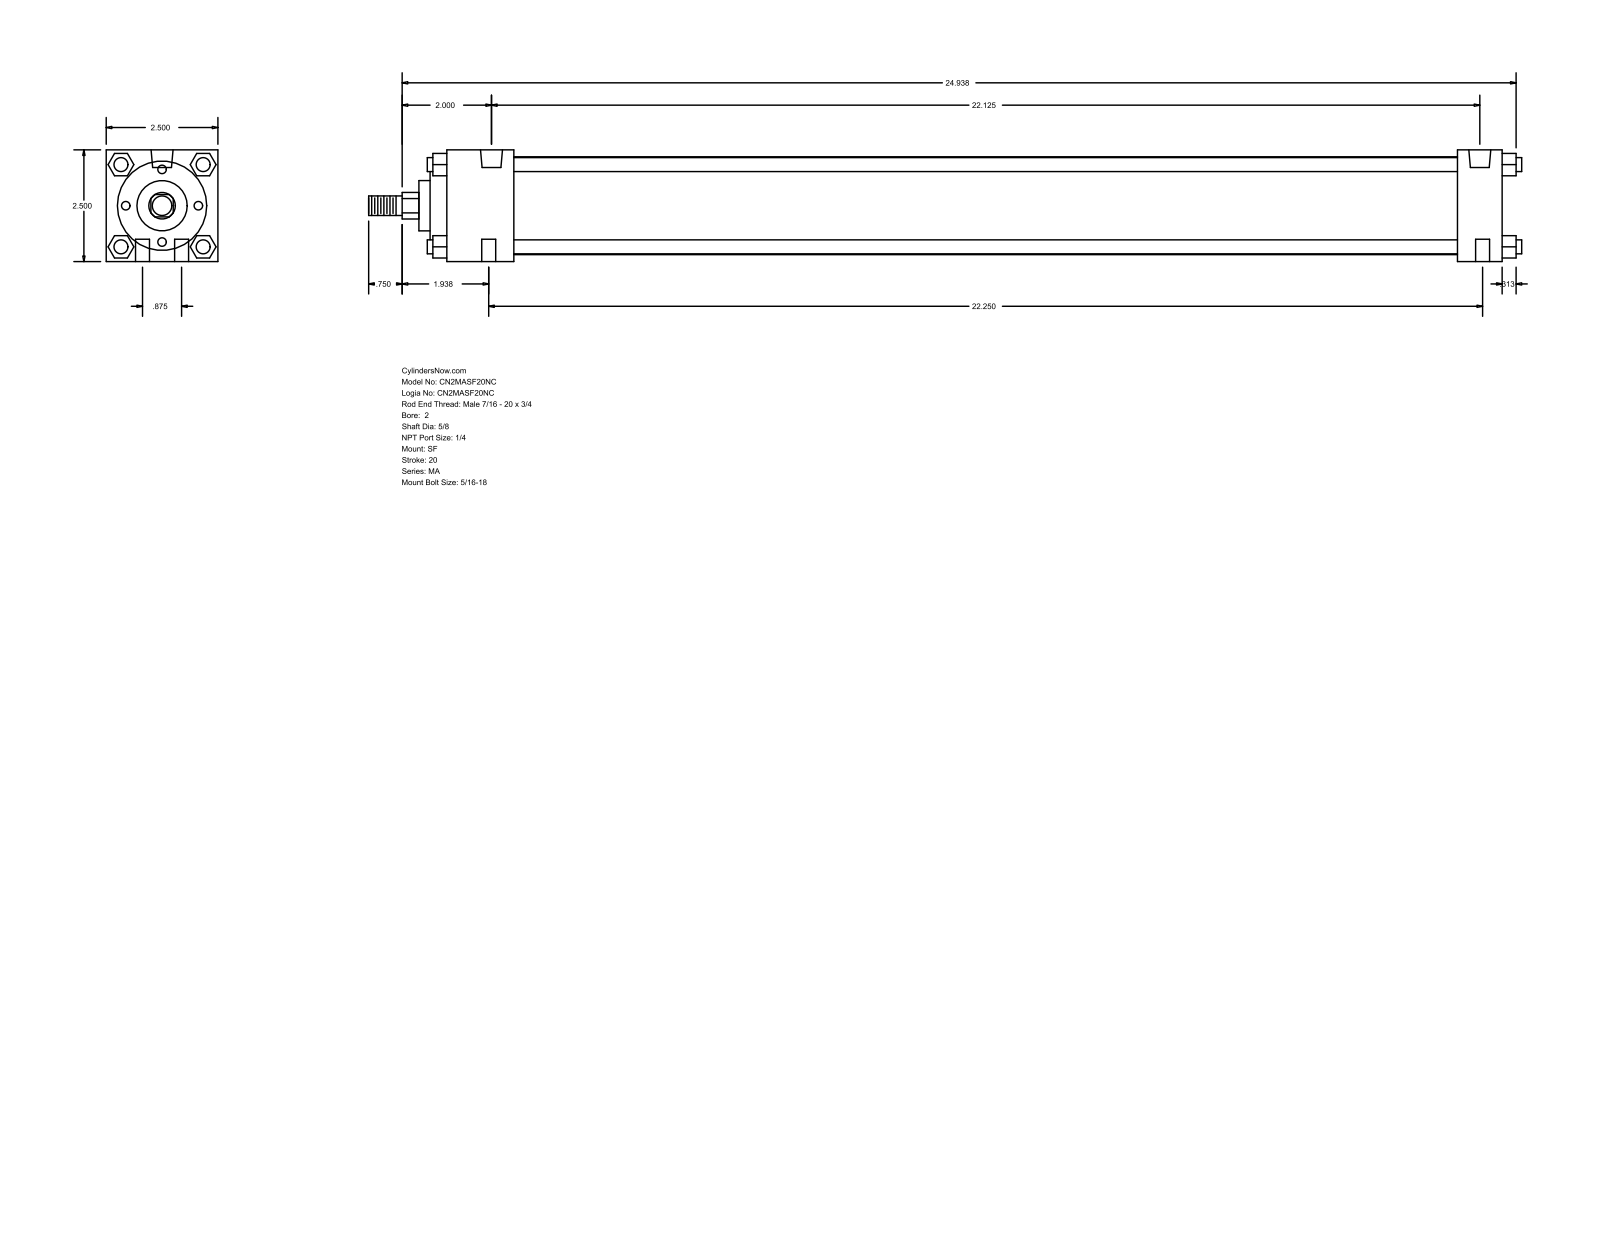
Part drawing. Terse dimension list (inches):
name: MA_SF__0200_0.625
written by: GSSL Pune (CONFIG_CONTROL_DESIGN)
unit: in
bodies: 0 solids, 126 faces (95 planar, 31 cylindrical, 0 other)
size: 25.813 × 2.5 × 2.5
holes: 6× ⌀0.313, 2× ⌀0.492
bosses: 4× ⌀0.313, 1× ⌀2.19, 1× ⌀2, 1× ⌀1.125, 1× ⌀0.625, 1× ⌀0.437
rounds: 1× R0.297
face distances: 2.5, 1, 0.5, 1.5, 23.625, 22.625, 21.125, 22.125, 0.375, 1.875
hole spacings: 0.442, 22.192, 0.875, 22.125, 22.25, 22.267
